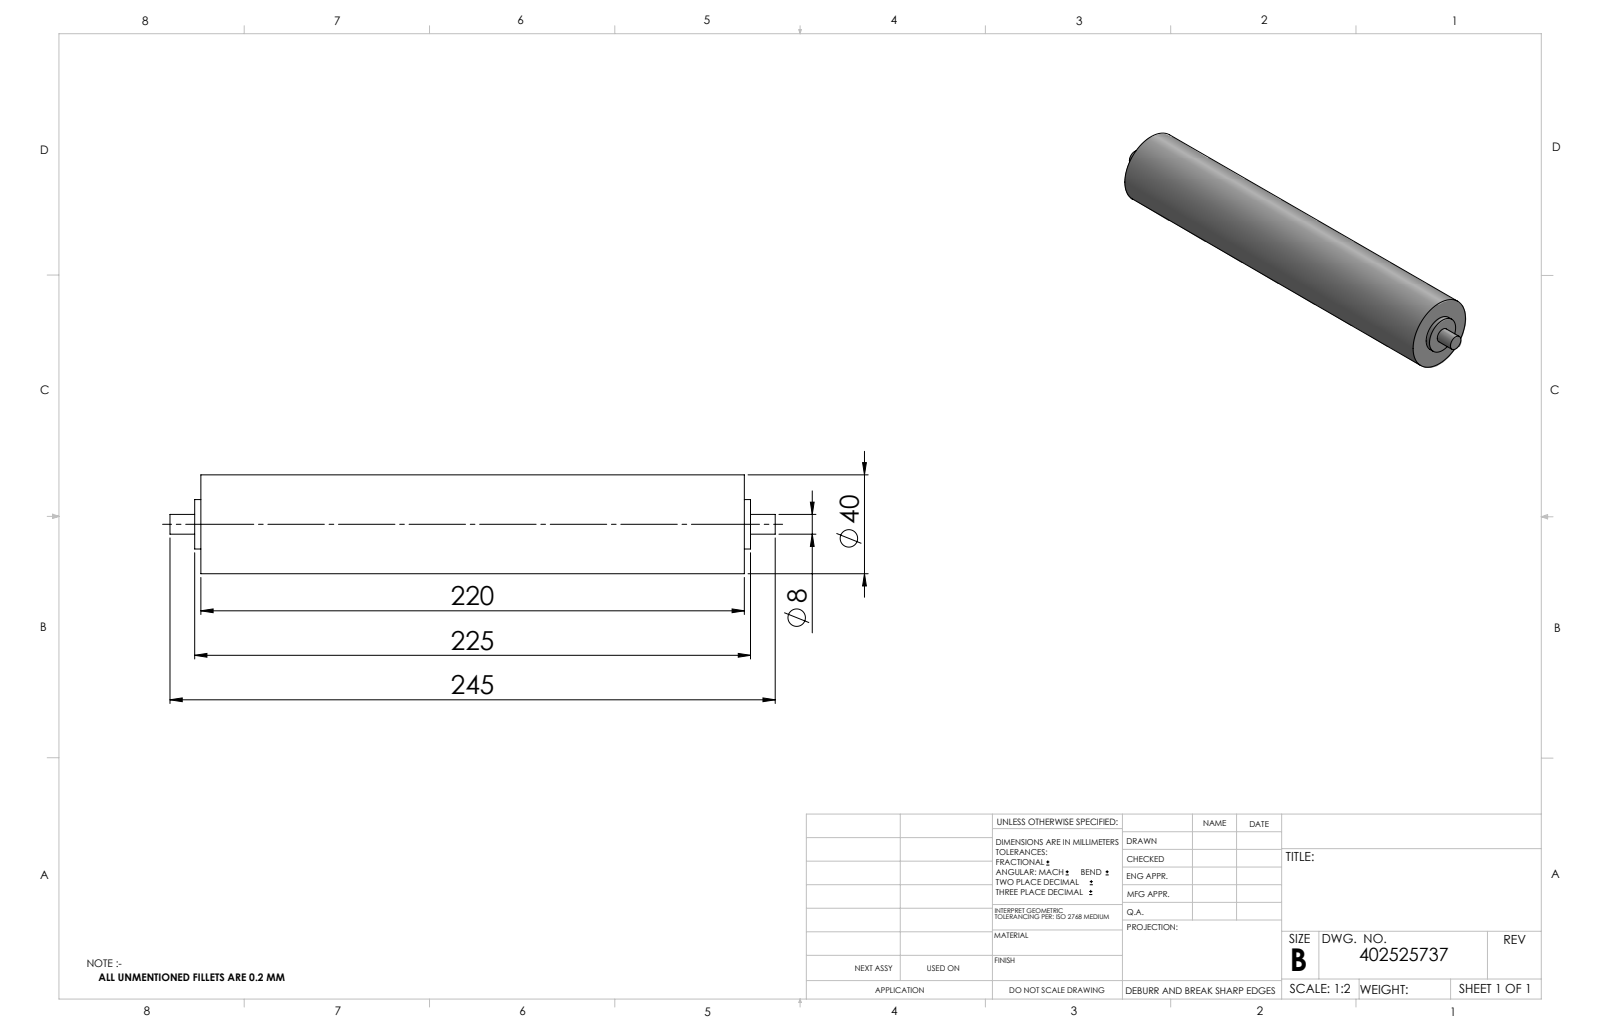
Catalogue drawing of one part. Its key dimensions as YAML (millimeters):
part_name: "402525737_c_1"
step_written_by: "SolidWorks 2014 (CONFIG_CONTROL_DESIGN)"
units: millimeters
bodies: {solids: 1, faces: 16, planar: 6, cylindrical: 10, other: 0}
overall_size: [245, 40, 40]
volume: 279036
surface_area: 30976
round_bosses_or_shafts:
  - {diameter: 40, count: 1}
  - {diameter: 20, count: 1}
  - {diameter: 8, count: 1}
face_to_face_distances: [220, 2.5, 222.5, 225, 10, 12.5, 232.5, 235, 245]
